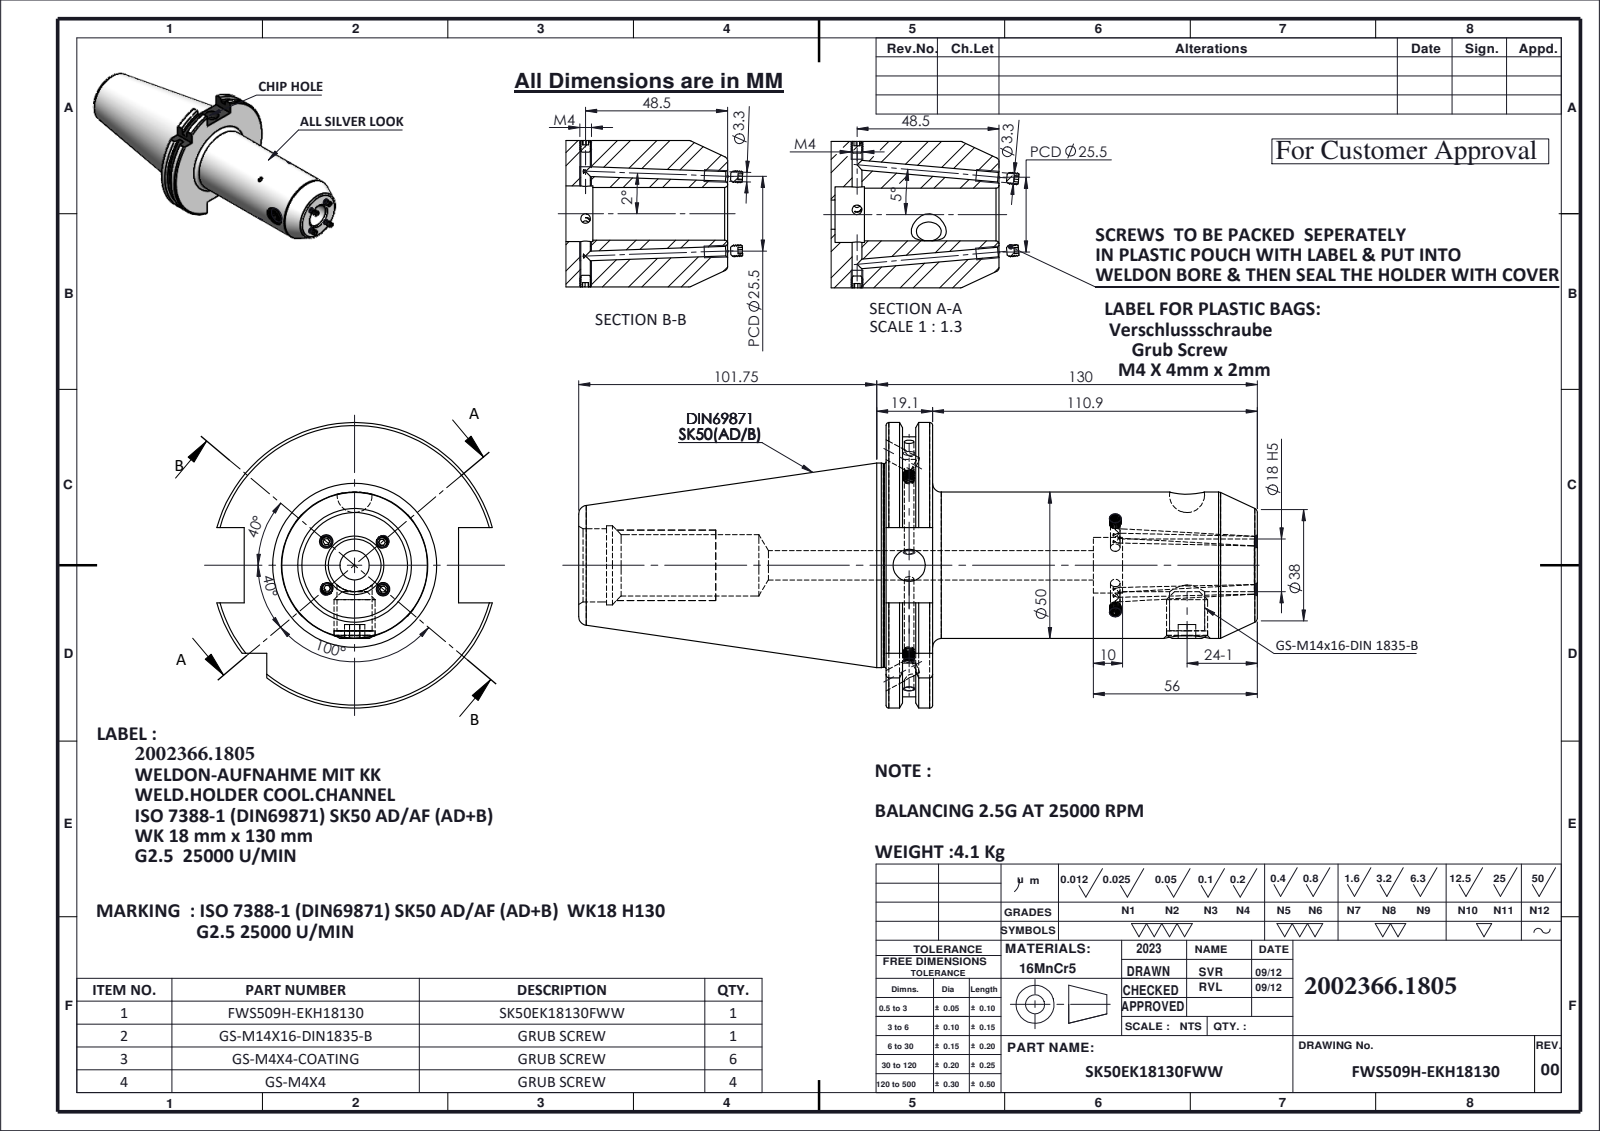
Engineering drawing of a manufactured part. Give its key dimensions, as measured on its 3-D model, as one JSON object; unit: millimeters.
{"part_name": "SK50EK18130FWW; FWS509H-EKH18130; GS-M4X4_DIN 913 - M4 x 4-N; GS-M14X16-DIN1835-B_ISO 4026 - M12 x 12-N (+1 more)", "step_written_by": "SolidWorks 2023 (CONFIG_CONTROL_DESIGN)", "units": "millimeters", "bodies": {"solids": 12, "faces": 648, "planar": 125, "cylindrical": 179, "other": 344}, "overall_size": [238.55, 97.5, 94.05], "volume_mm3": 524475, "surface_area_mm2": 69611, "round_holes": [[3.3, 9], [6, 2], [10, 1], [11, 1], [12, 1], [14, 1], [18, 1], [19, 1], [21, 1], [25, 1], [27, 1]], "round_bosses_or_shafts": [[4, 10], [69.85, 1], [69.45, 1], [50, 1]], "partial_cylinders_radius": [[44.9, 1], [48.75, 1]], "face_to_face_distances": [15.9, 126.8, 110.9, 5.65, 10.25, 121.15, 10.14, 4.49, 5.76, 116.66]}
